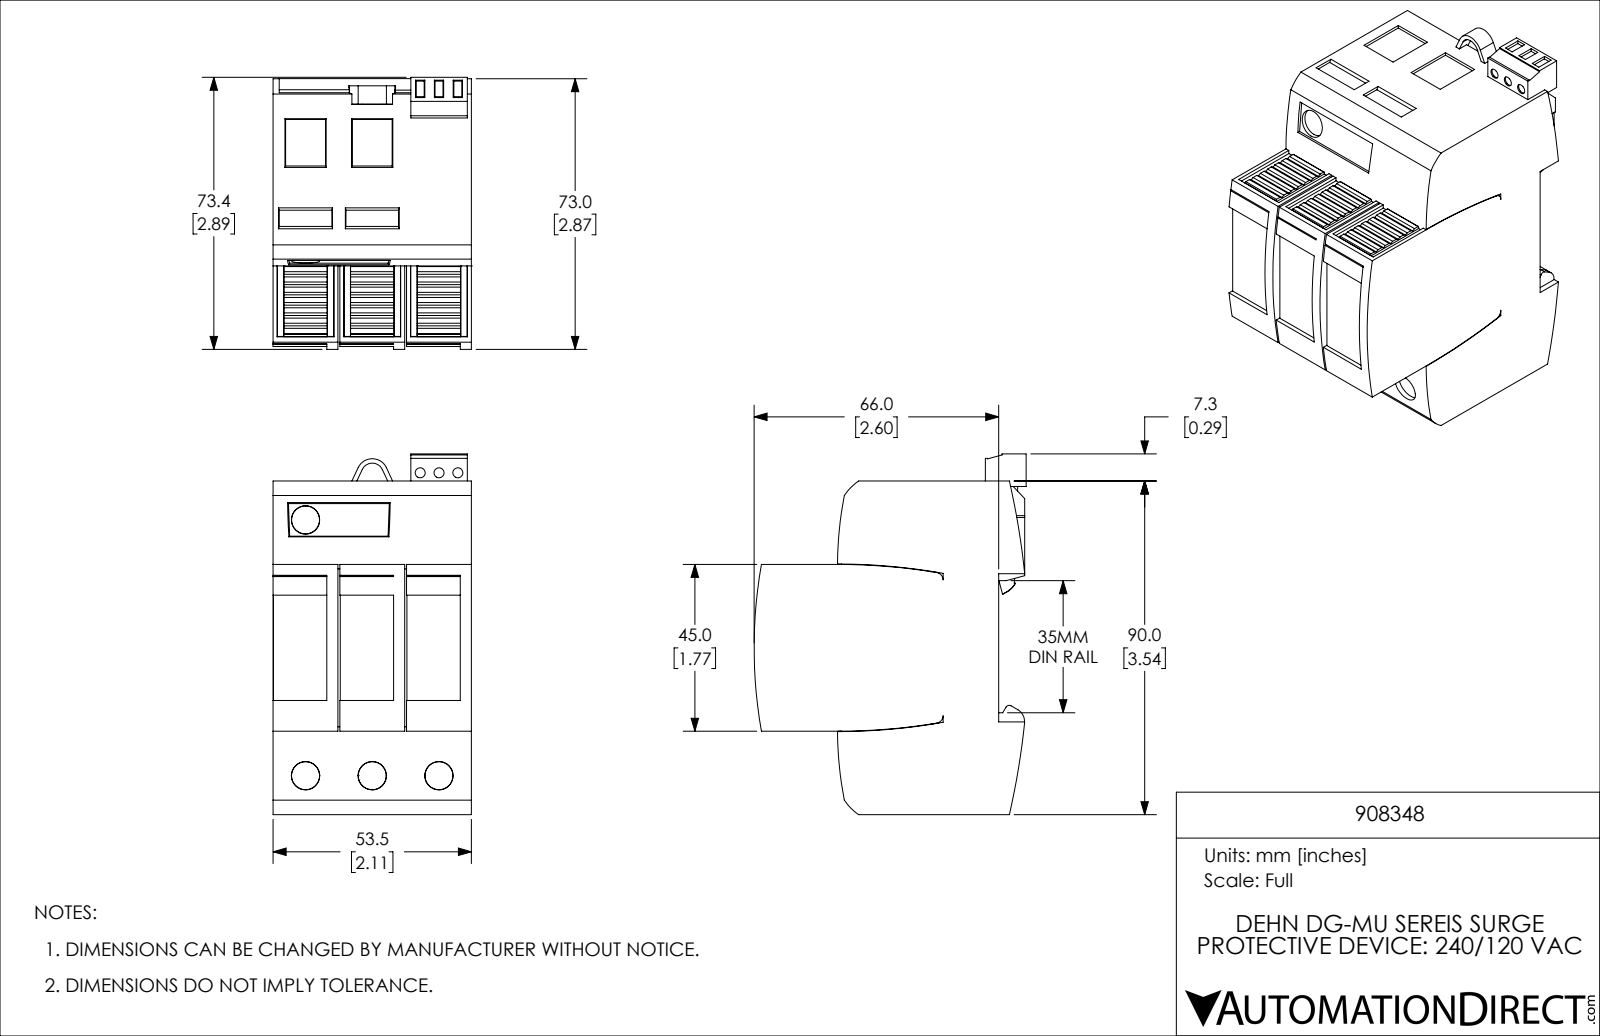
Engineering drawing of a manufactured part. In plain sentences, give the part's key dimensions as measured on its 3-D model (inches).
The part is named "908348". Its 3-D file was written by "SolidWorks 2024 (AUTOMOTIVE_DESIGN)". It is 1 solid with 178 faces: 142 planar, 25 cylindrical and 11 other. Overall it measures 3.827 by 2.89 by 2.815 inches. Its volume is 22.42 cubic inches and its surface area 54.33 square inches. Round holes: 3 of diameter 0.106. Partial cylindrical surfaces (rounded edges, fillets, slot ends): 2 of radius 0.079, 2 of radius 3.937, 1 of radius 0.039, 1 of radius 0.138, 1 of radius 0.165, 1 of radius 0.551, 1 of radius 0.551, 1 of radius 3.878. The main face-to-face distances are 2.815, 0.886, 2.657, 3.543, 2.518, 1.772, 0.276, 2.794, 2.632, 0.026. The hole center spacings are 0.2, 0.2, 0.4.
